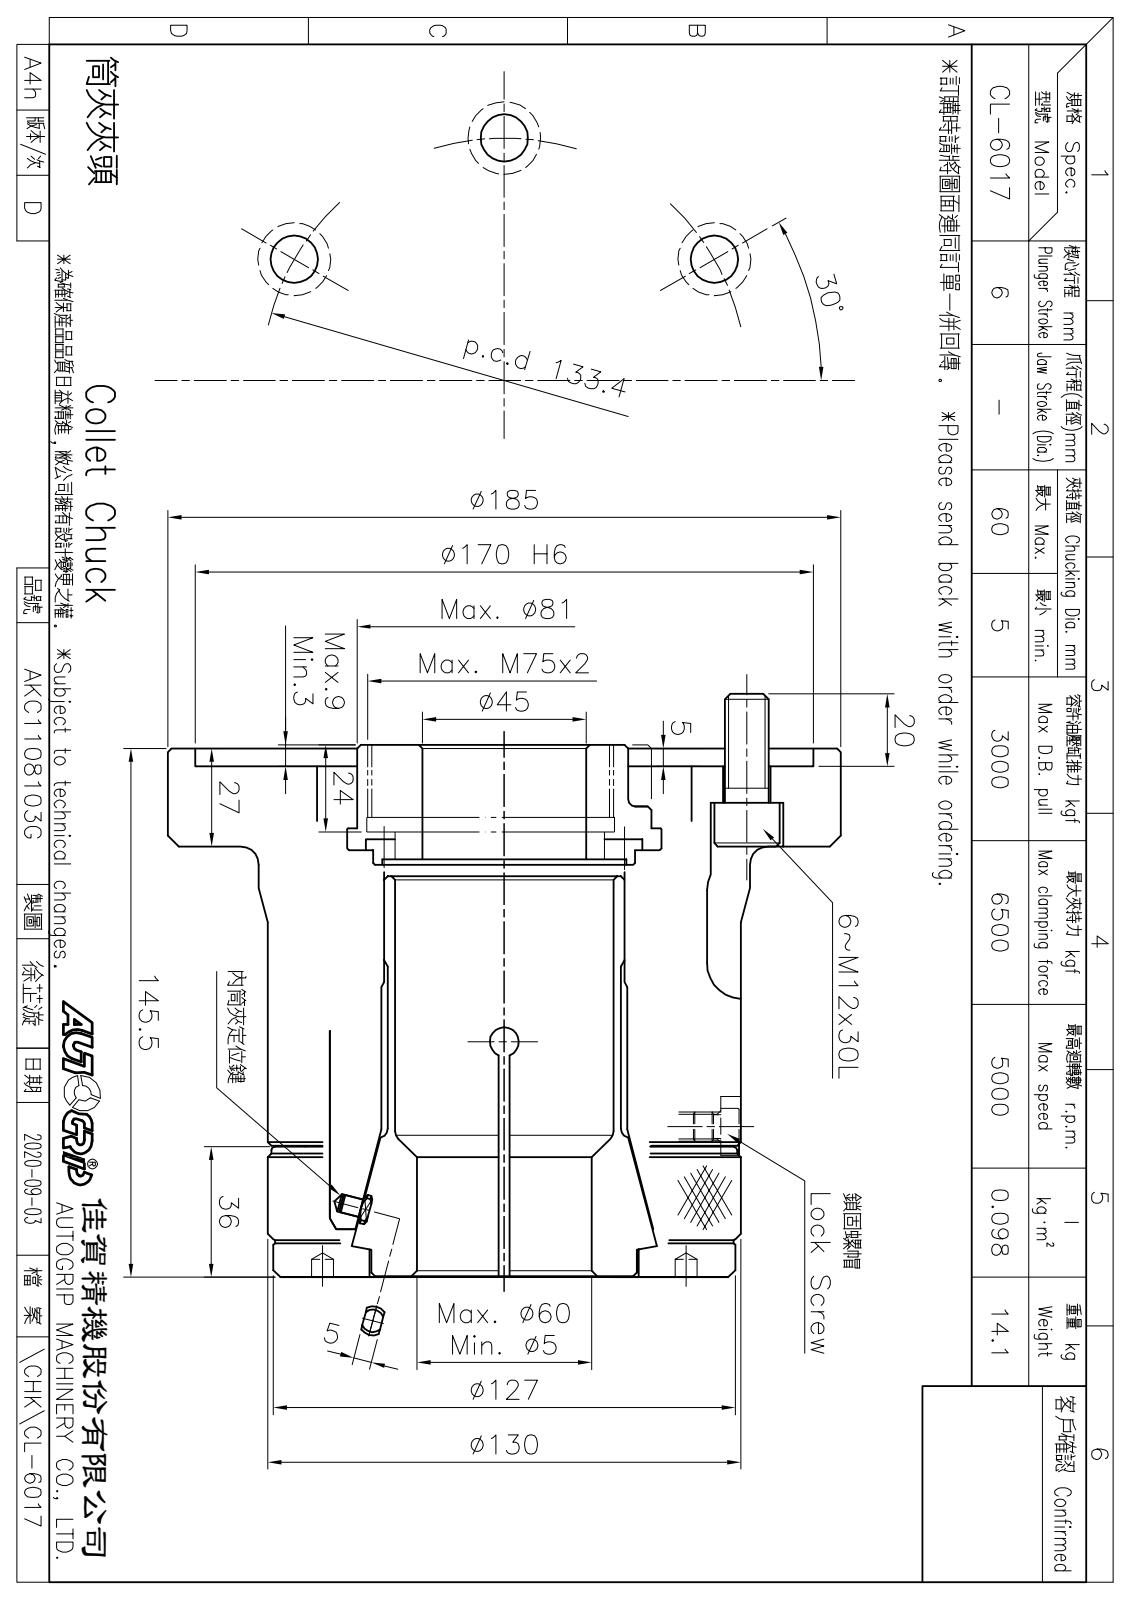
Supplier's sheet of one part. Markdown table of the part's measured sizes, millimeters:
| quantity | value |
| --- | --- |
| part name | CF-CL-6017-02000; CF-CL-6017-05020; 圓頭內六角螺栓_M12x30; CF-CL-6017-03010 (+4 more) |
| STEP written by | SolidWorks 2020 (CONFIG_CONTROL_DESIGN) |
| units | millimeters |
| bodies | 12 solids, 311 faces (140 planar, 77 cylindrical, 94 other) |
| overall size | 185 × 185 × 160.5 |
| volume | 1 569 000 mm³ |
| surface area | 295 300 mm² |
| round holes (diameter × count) | 13.5 × 6, 20 × 6, 6 × 2, 5 × 1, 6.8 × 1, 60 × 1, 66 × 1, 67 × 1, 67.5 × 1, 72 × 1, 73 × 1, 74 × 1 |
| round bosses / shafts (diameter × count) | 18 × 6, 12 × 6, 185 × 1, 130 × 1, 128 × 1, 127 × 1, 126 × 1, 109.5 × 1 |
| partial cylindrical surfaces (radius × count) | 10 × 6, 8.5 × 3, 4 × 1, 8 × 1, 8.25 × 1, 67.5 × 1 |
| main face-to-face distances | 22, 20, 5, 2, 10, 120.5, 140.5, 118.5, 104.3, 12 |
| hole center spacings | 66.7, 34.24, 83.36, 115.53, 50, 112.8, 112.81, 115.52 |
